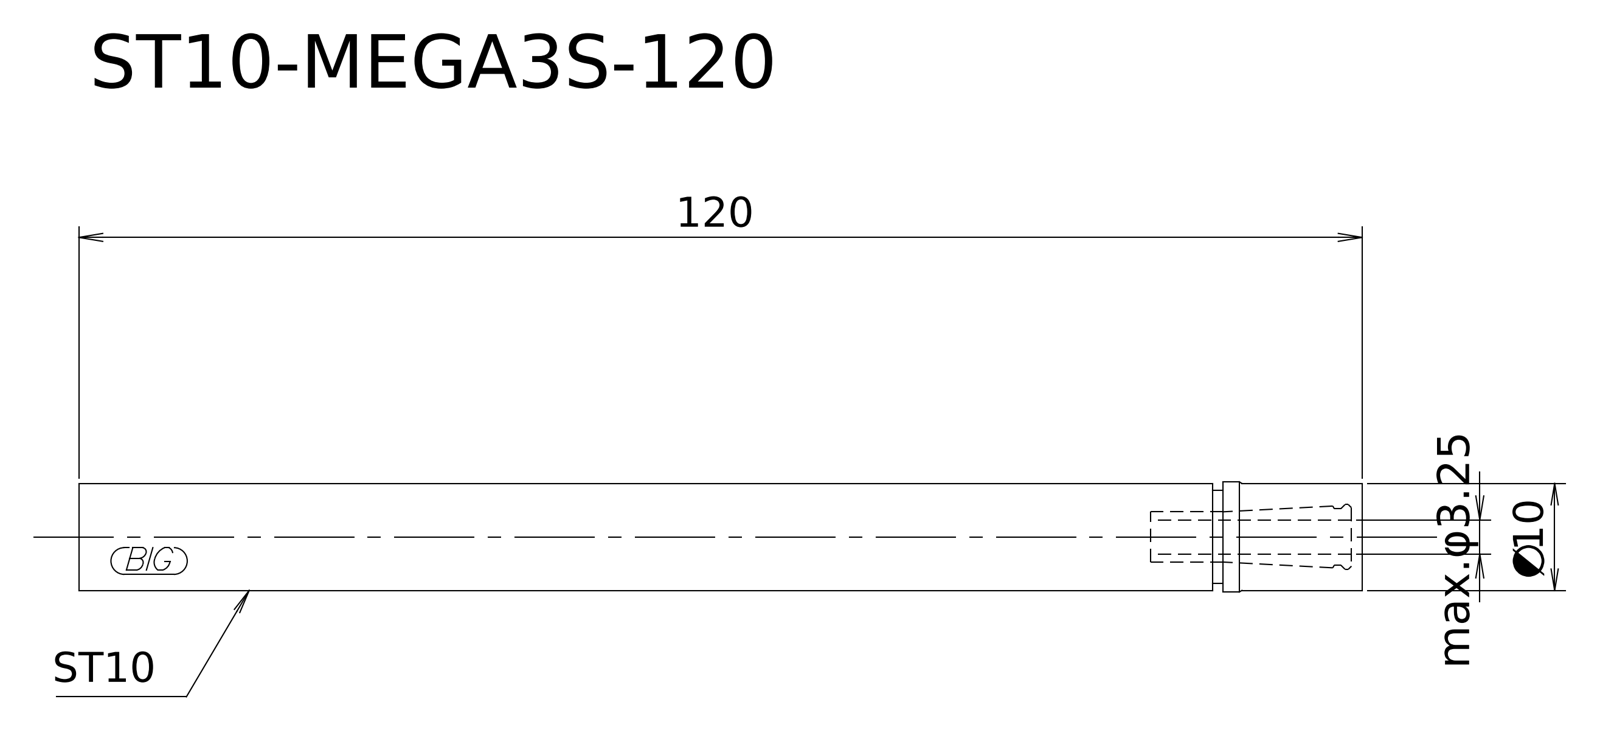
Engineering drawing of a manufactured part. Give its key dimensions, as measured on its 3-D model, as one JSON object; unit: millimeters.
{"step_written_by": "Kubotek KeyCreator V8.5.1 (14335) (CONFIG_CONTROL_DESIGN)", "units": "millimeters", "bodies": {"solids": 1, "faces": 9, "planar": 3, "cylindrical": 4, "other": 2}, "overall_size": [120, 10.3, 10.3], "volume_mm3": 9411, "surface_area_mm2": 3960, "round_bosses_or_shafts": [[10.3, 1], [10, 1], [8.7, 1]], "face_to_face_distances": [120, 13, 107]}
